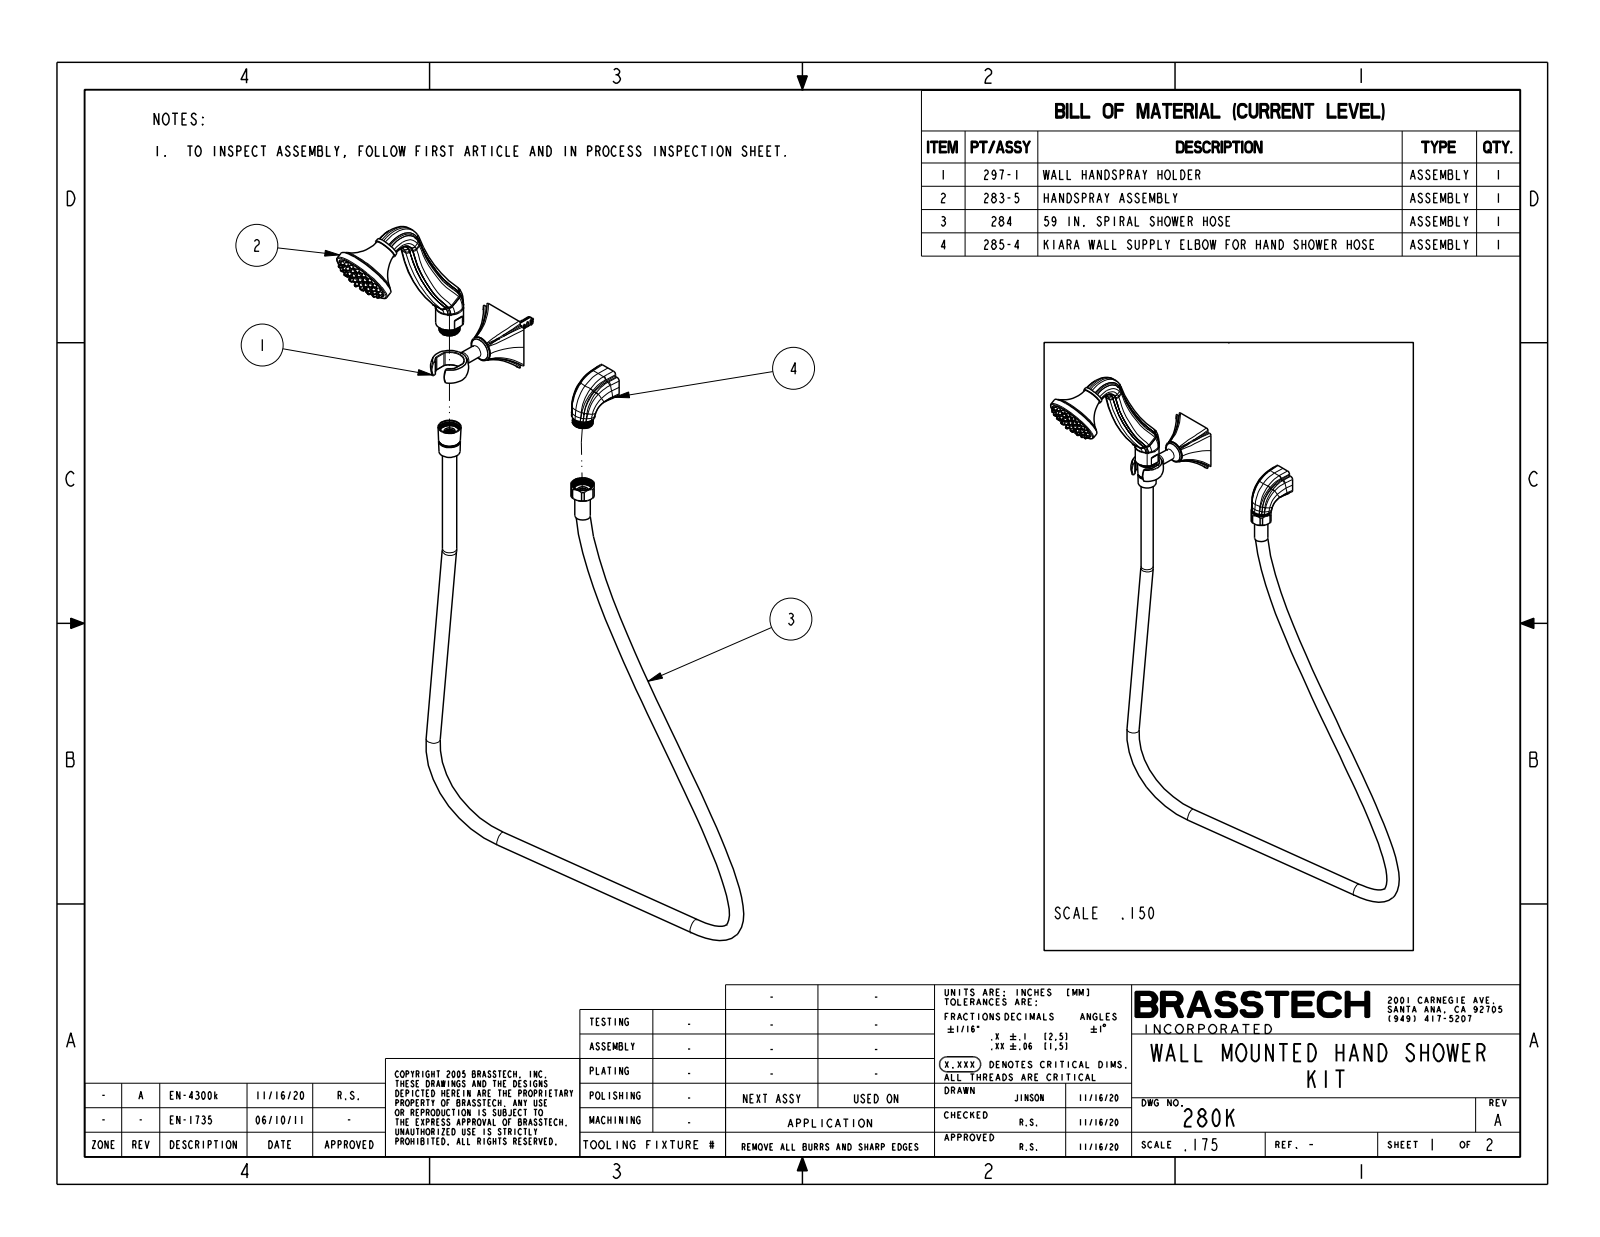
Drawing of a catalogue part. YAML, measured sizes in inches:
part_name: "280K"
step_written_by: "CREO PARAMETRIC BY PTC INC, 2018400 (CONFIG_CONTROL_DESIGN)"
units: inches
bodies: {solids: 2, faces: 1286, planar: 192, cylindrical: 317, other: 777}
overall_size: [26.56, 13.985, 9.274]
volume: 28
surface_area: 167.7
round_holes:
  - {diameter: 0.039, count: 51}
  - {diameter: 0.079, count: 51}
  - {diameter: 0.656, count: 1}
round_bosses_or_shafts:
  - {diameter: 0.56, count: 3}
  - {diameter: 0.79, count: 2}
  - {diameter: 2.49, count: 1}
  - {diameter: 2.3, count: 1}
  - {diameter: 2.05, count: 1}
  - {diameter: 1.79, count: 1}
  - {diameter: 1.29, count: 1}
  - {diameter: 1.1, count: 1}
partial_cylinders:
  - {radius: 0.065, count: 50}
  - {radius: 0.02, count: 6}
  - {radius: 0.125, count: 4}
  - {radius: 0.05, count: 2}
  - {radius: 0.494, count: 1}
  - {radius: 0.547, count: 1}
  - {radius: 0.56, count: 1}
face_to_face_distances: [0.275, 1.182, 1.322, 0.14, 0.902, 0.013, 1.013, 0.557, 0.625, 0.765]
hole_center_spacings: [0.618, 1.976, 1, 0.313, 1.176, 1.618, 1.414, 1.782]
